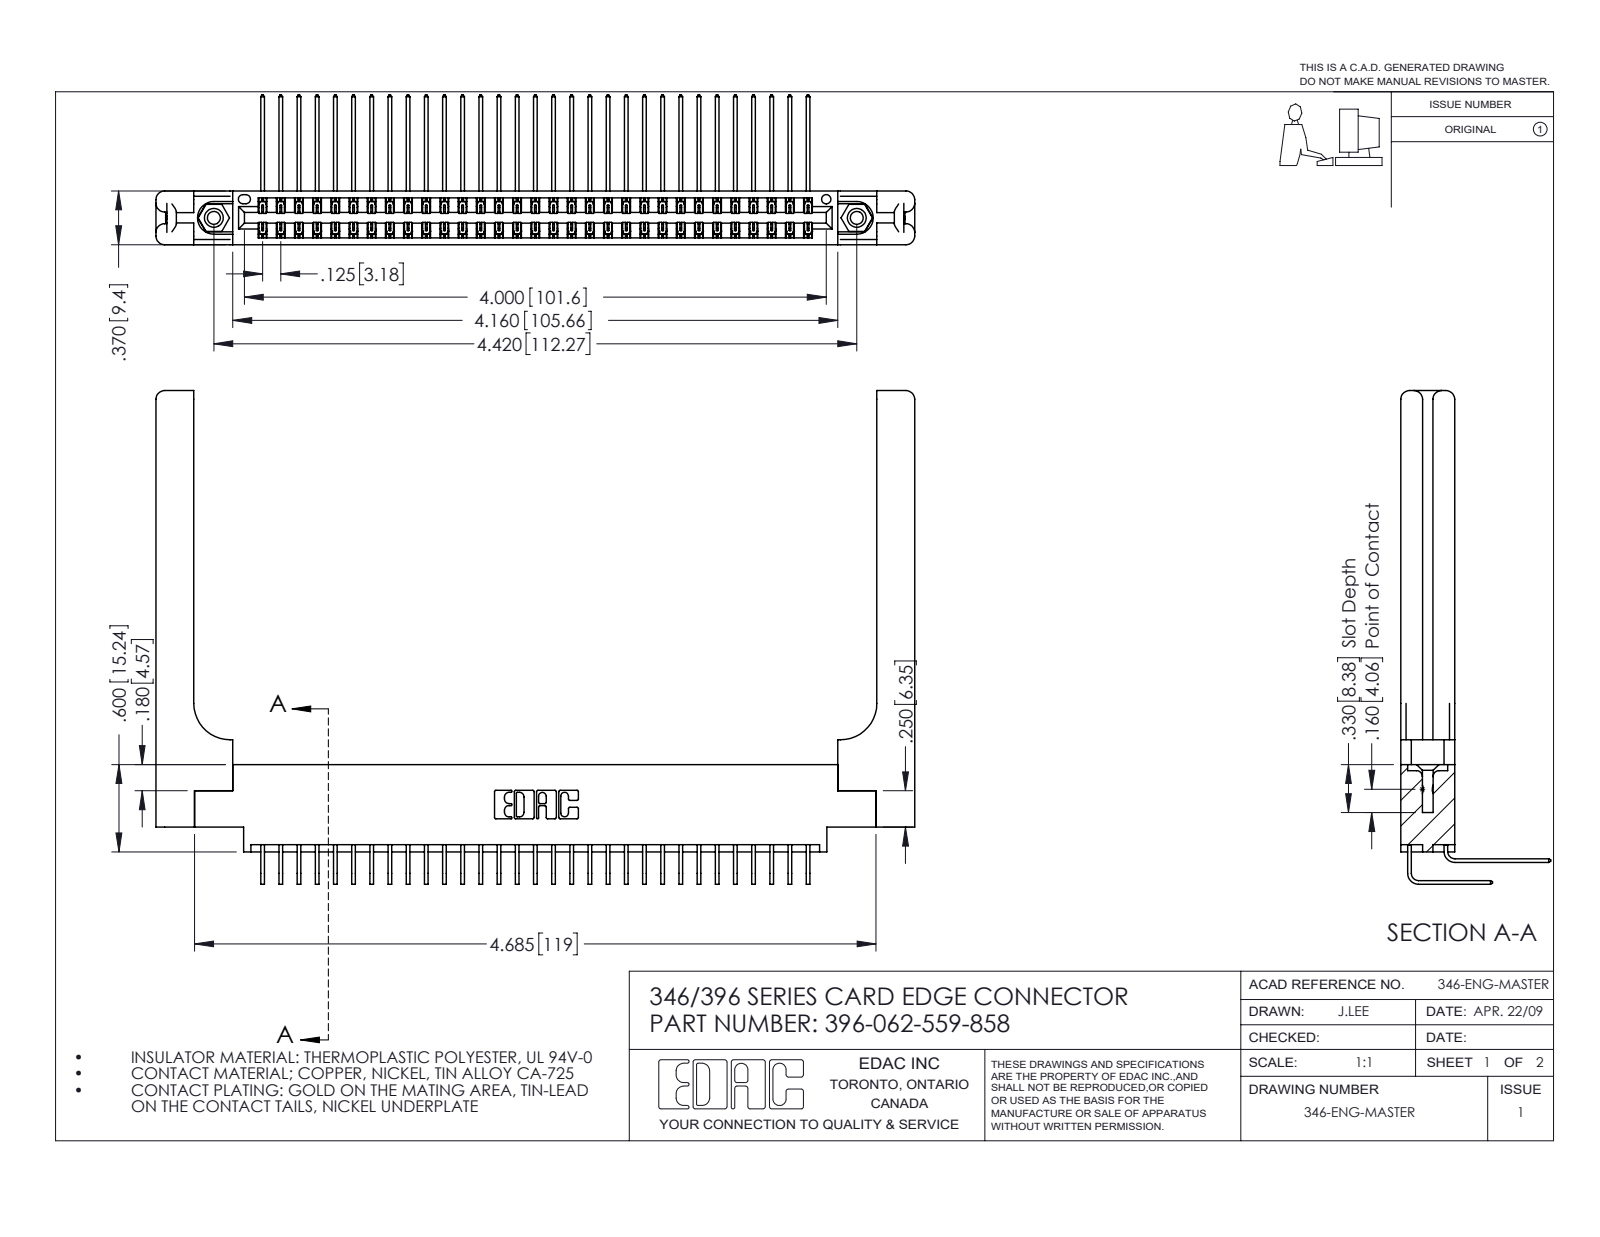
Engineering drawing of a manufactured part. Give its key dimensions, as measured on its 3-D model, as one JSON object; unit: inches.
{"part_name": "345-292-001_559 Tail - 2; 346 Part_0.170 Offset - 0.156 Dia-TH; 396-062-559-858; 346-220-058_345-220-058 (+2 more)", "step_written_by": "SolidWorks 2016 (CONFIG_CONTROL_DESIGN)", "units": "inches", "bodies": {"solids": 67, "faces": 3730, "planar": 2522, "cylindrical": 1148, "other": 60}, "overall_size": [5.216, 3.393, 1.03], "volume_in3": 1.253, "surface_area_in2": 38.15, "round_holes": [[0.089, 2], [0.125, 2], [0.156, 2], [0.064, 1]], "round_bosses_or_shafts": [[0.155, 2]], "partial_cylinders_radius": [[0.006, 93], [0.01, 22], [0.06, 16], [0.007, 6], [0.031, 6], [0.026, 3], [0.014, 2], [0.022, 2]], "face_to_face_distances": [0.37, 0.048, 0.072, 0.322, 0.025, 0.148, 0.15, 0.25, 0.298, 0.275], "hole_center_spacings": [0.246, 4.212, 4.42]}
